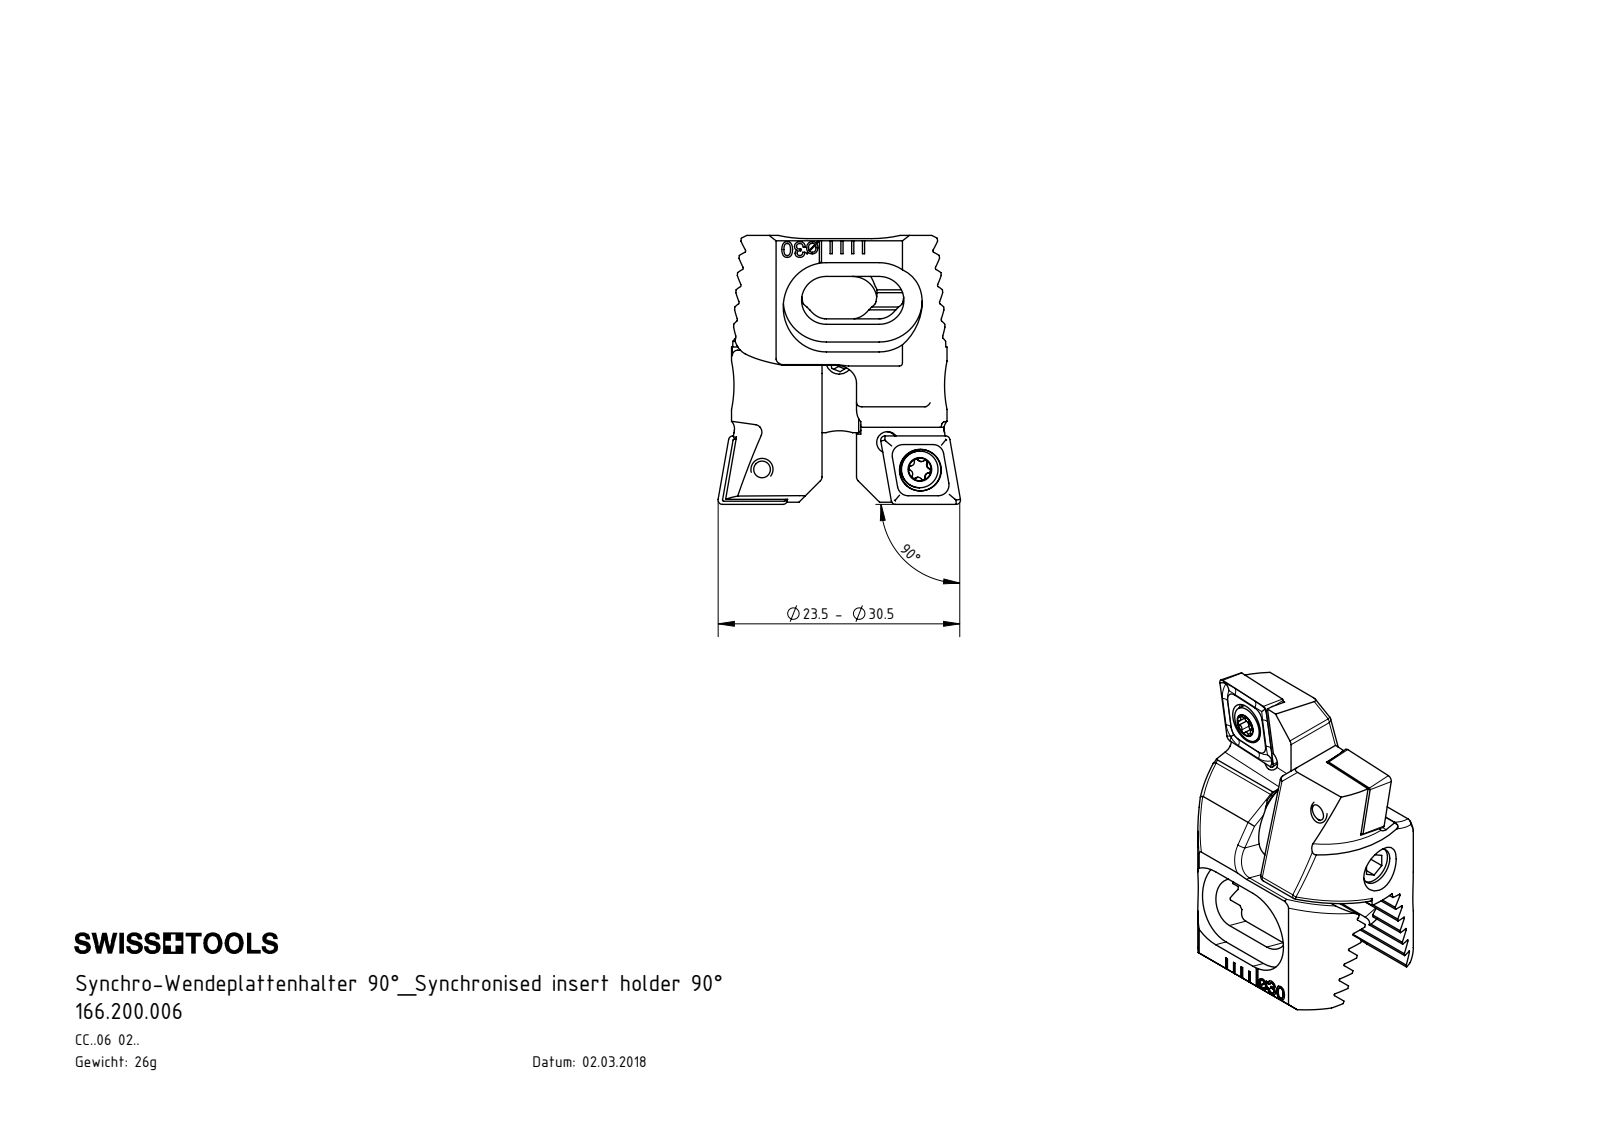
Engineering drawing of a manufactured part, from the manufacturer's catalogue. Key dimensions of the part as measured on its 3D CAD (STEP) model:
Part name (STEP PRODUCT): 166.200.006; Z20-ER3.002.004_A; Z20-WCA.003.015_A; Z20-WCA.001.015_A (+4 more)
STEP written by: SolidWorks 2017 (CONFIG_CONTROL_DESIGN)
Units: millimetres
Bodies: 11 solids, 485 faces (189 planar, 158 cylindrical, 138 other)
Overall size (bounding box): 24.95 × 22.42 × 16.3
Volume: 3 171 mm³ · Surface area: 3 798 mm²
Round holes (diameter × count): ⌀1 ×3, ⌀2.5 ×3, ⌀2 ×2, ⌀2.05 ×2, ⌀2.8 ×2, ⌀3.85 ×2, ⌀3.5 ×1, ⌀9.1 ×1
Round bosses / shafts (diameter × count): ⌀3 ×4, ⌀3.4 ×2, ⌀2.5 ×2, ⌀8.8 ×1, ⌀4 ×1
Partial cylindrical surfaces — rounded edges, fillets, slot ends (radius × count): R0.12 ×12, R0.21 ×12, R0.36 ×10, R1 ×8, R0.5 ×4, R2.3 ×4, R4 ×4, R0.36 ×2
Main face-to-face distances: 1.43, 2.86, 4.29, 4, 5.72, 2.57, 3.85, 7.14, 5.71, 0.42
Hole centre spacings: 3.99, 4.09, 12.02, 12.12, 14.88, 2, 5.99, 6
